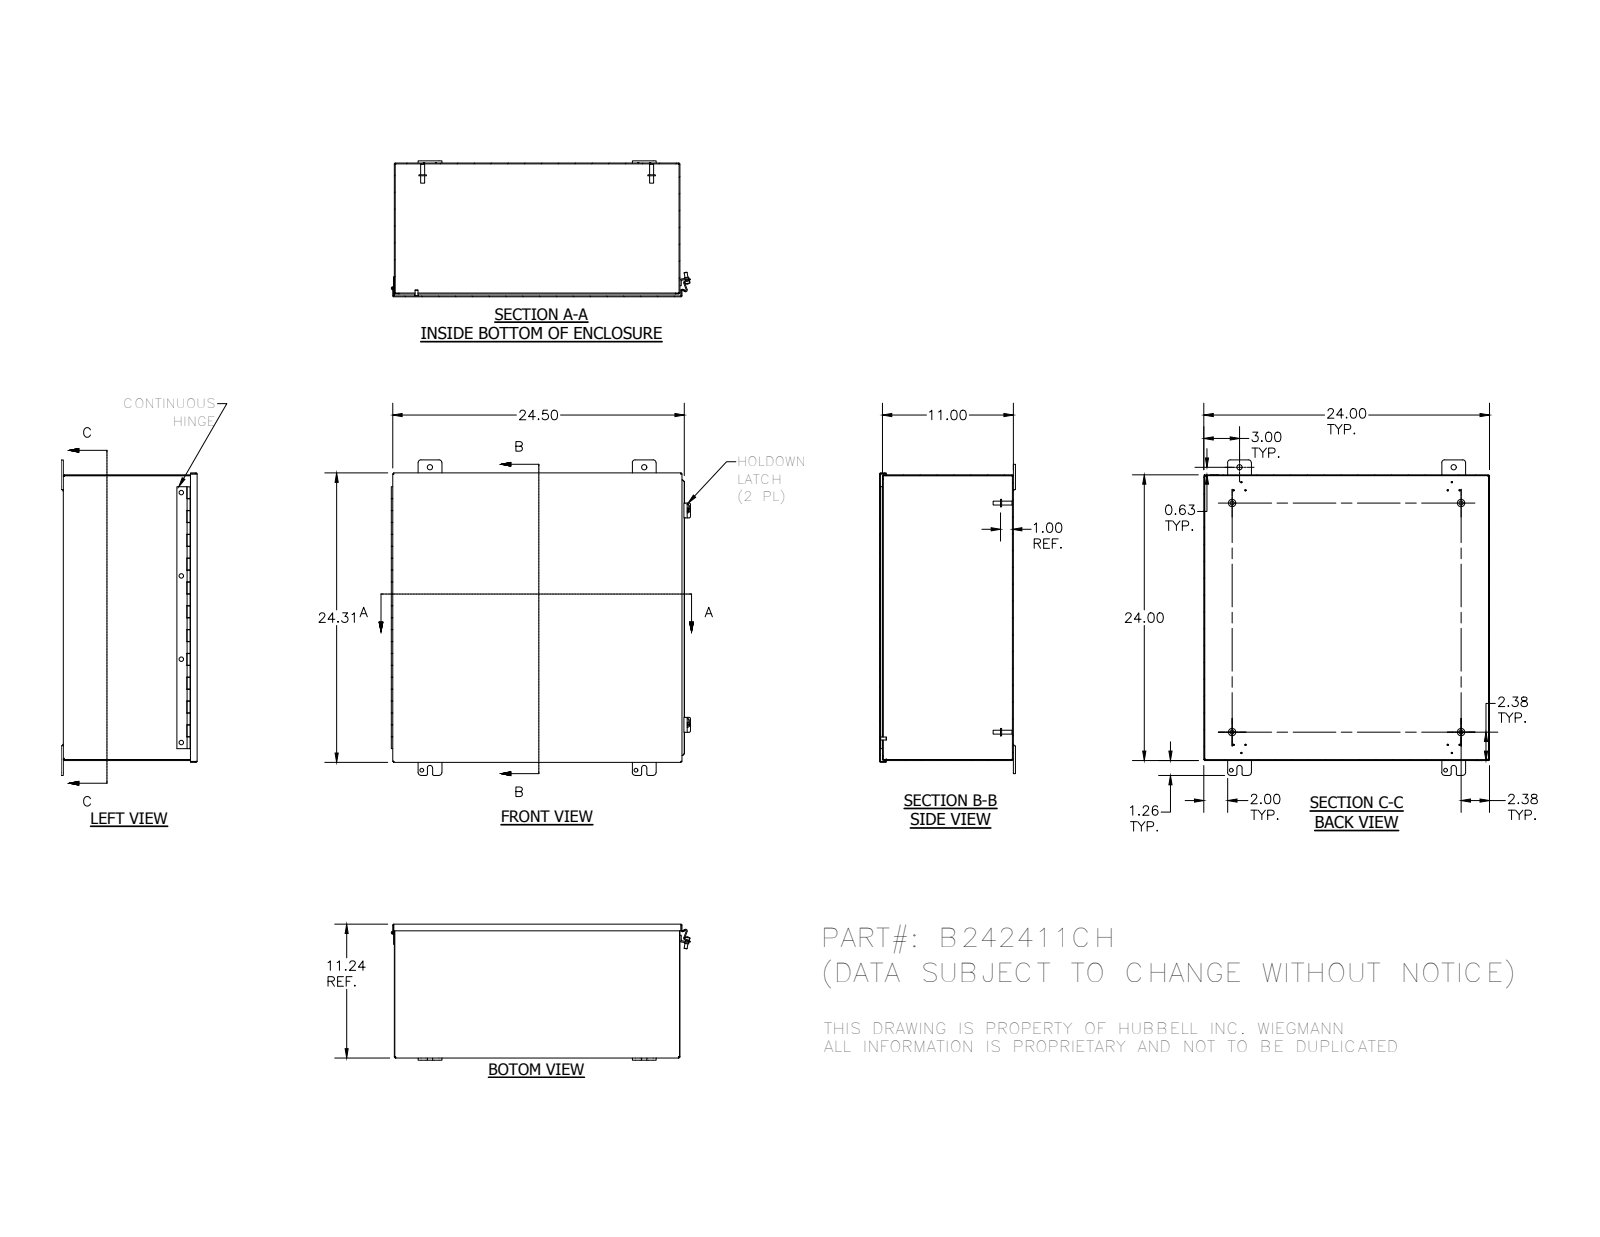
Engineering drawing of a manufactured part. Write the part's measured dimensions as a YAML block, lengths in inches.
part_name: "B242411CH; B242411CHBKP; B2424CHLID; H6010101 (+8 more)"
step_written_by: "Autodesk Inventor 2012 (AUTOMOTIVE_DESIGN)"
units: inches
bodies: {solids: 20, faces: 649, planar: 395, cylindrical: 185, other: 69}
overall_size: [26.505, 25.136, 11.423]
volume: 176.4
surface_area: 4761
round_holes:
  - {diameter: 0.11, count: 4}
  - {diameter: 0.313, count: 4}
  - {diameter: 0.375, count: 4}
  - {diameter: 0.438, count: 4}
  - {diameter: 0.196, count: 2}
  - {diameter: 0.125, count: 1}
  - {diameter: 0.125, count: 1}
round_bosses_or_shafts:
  - {diameter: 0.625, count: 4}
  - {diameter: 0.33, count: 4}
  - {diameter: 0.25, count: 4}
  - {diameter: 0.41, count: 2}
  - {diameter: 0.344, count: 2}
  - {diameter: 0.337, count: 1}
  - {diameter: 0.12, count: 1}
partial_cylinders:
  - {radius: 0.125, count: 16}
  - {radius: 0.25, count: 16}
  - {radius: 0.031, count: 8}
  - {radius: 0.063, count: 8}
  - {radius: 0.07, count: 8}
  - {radius: 0.105, count: 8}
  - {radius: 0.016, count: 5}
  - {radius: 0.09, count: 5}
face_to_face_distances: [0.074, 11.169, 23.926, 11.243, 11.095, 24, 23.852, 0.137, 24.063, 10.926]
hole_center_spacings: [18, 30.004, 1.593, 7, 24.005, 0.75, 14, 17.372]
